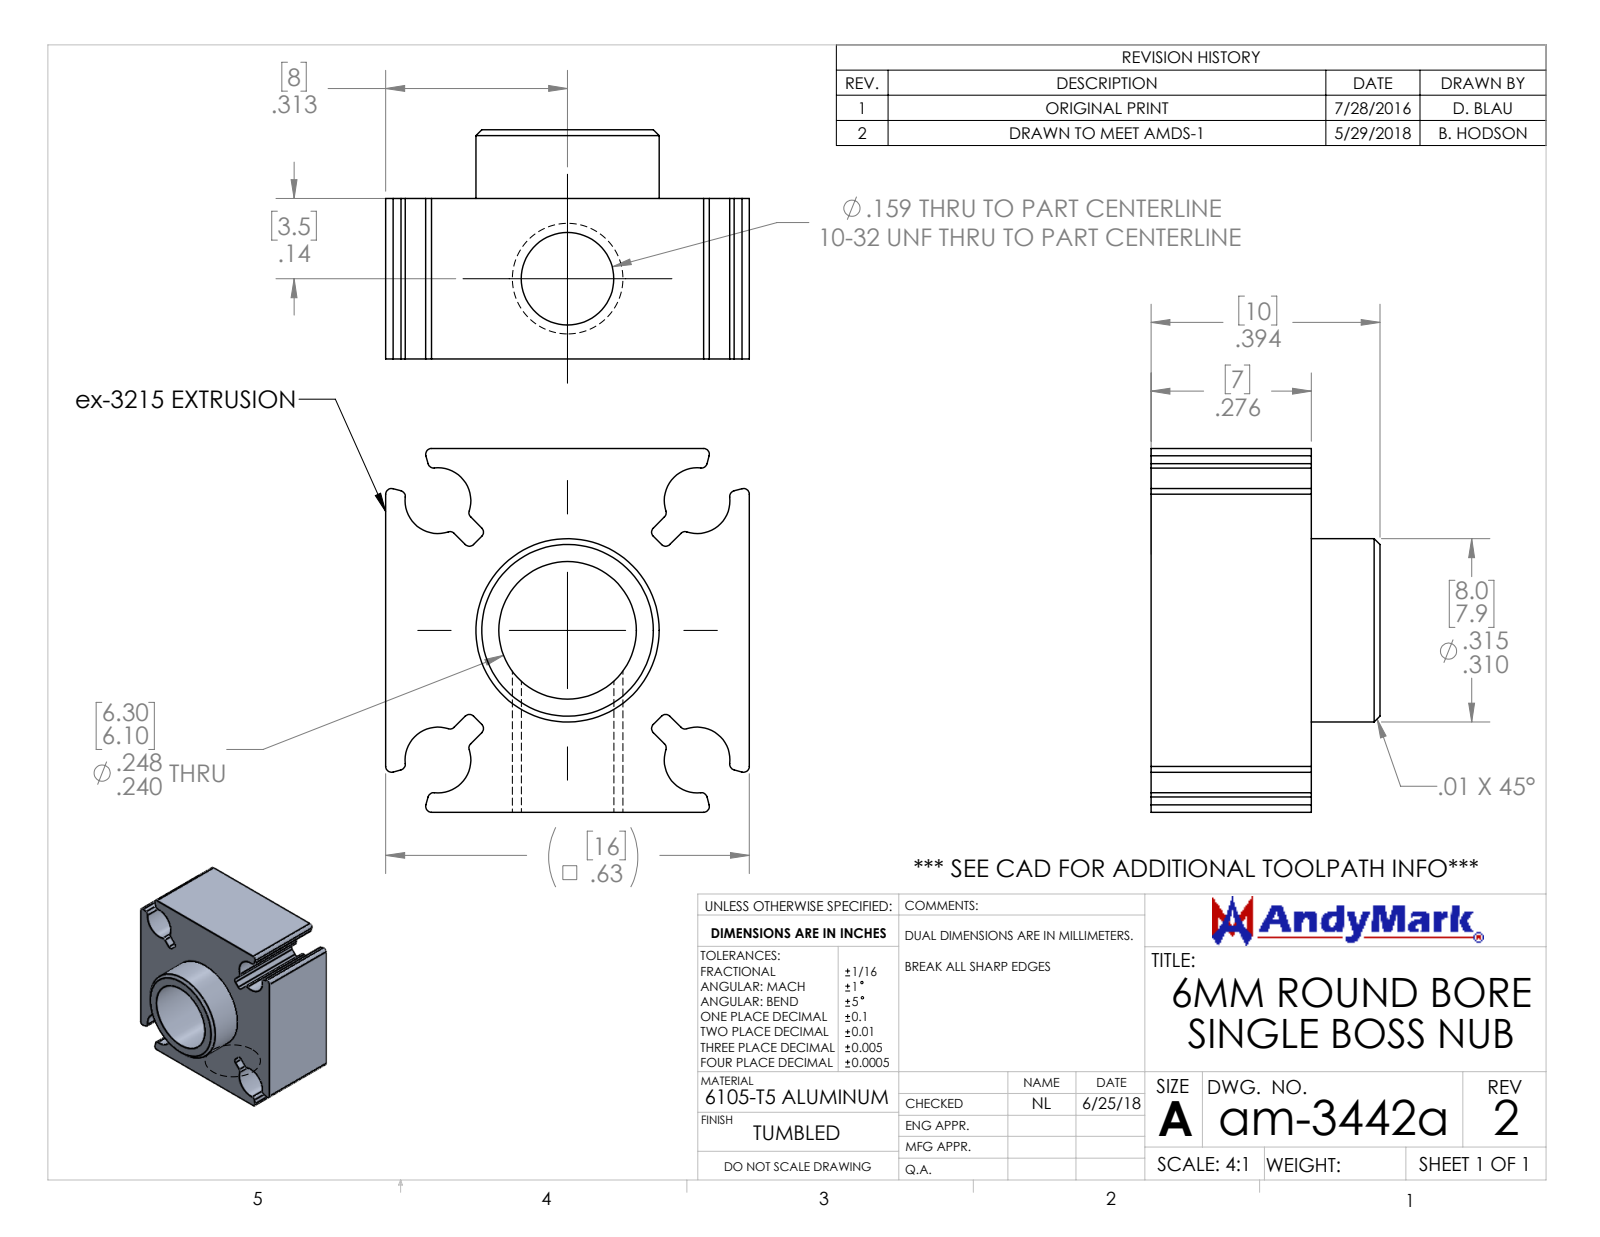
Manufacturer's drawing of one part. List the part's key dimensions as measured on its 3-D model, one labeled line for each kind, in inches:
Part name (STEP PRODUCT): am-3442a 6mm Round Single Boss Nub REV2
STEP written by: SolidWorks 2017 (AUTOMOTIVE_DESIGN)
Units: inches
Bodies: 1 solid, 87 faces (27 planar, 58 cylindrical, 2 other)
Overall size (bounding box): 0.625 × 0.625 × 0.394
Volume: 0.078 in³ · Surface area: 2.04 in²
Round holes (diameter × count): ⌀0.159 ×1, ⌀0.236 ×1
Round bosses / shafts (diameter × count): ⌀0.315 ×1
Partial cylindrical surfaces — rounded edges, fillets, slot ends (radius × count): R0.01 ×32, R0.056 ×4
Main face-to-face distances: 0.276, 0.625, 0.625, 0.04, 0.394, 0.118, 0.198, 0.238, 0.315, 0.437
